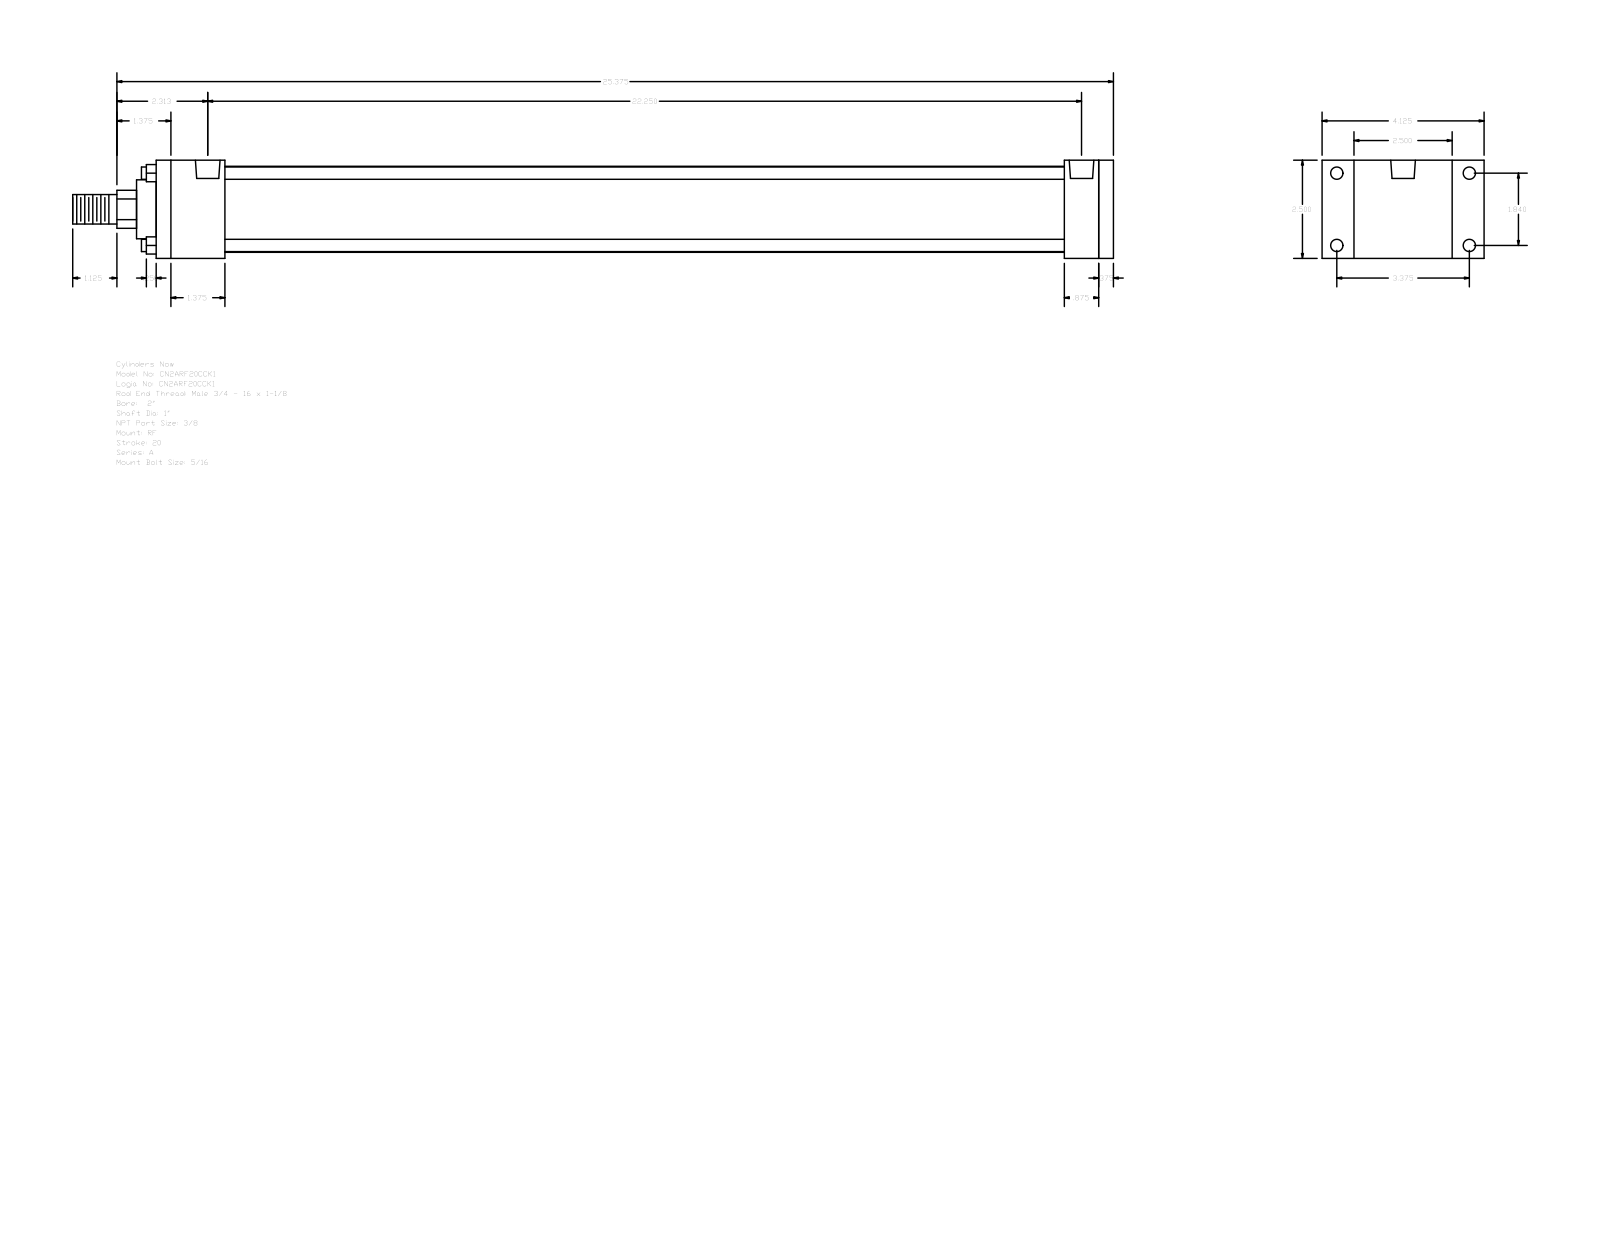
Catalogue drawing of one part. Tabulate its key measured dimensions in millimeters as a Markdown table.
| quantity | value |
| --- | --- |
| part name | A_RF__0200_1 |
| STEP written by | GSSL Pune (CONFIG_CONTROL_DESIGN) |
| units | millimeters |
| bodies | 0 solids, 92 faces (64 planar, 28 cylindrical, 0 other) |
| overall size | 673.1 × 104.78 × 63.5 |
| round holes (diameter × count) | 5.56 × 4, 7.94 × 4, 15.93 × 2 |
| round bosses / shafts (diameter × count) | 7.94 × 4, 55.63 × 1, 38.1 × 1, 25.4 × 1, 19.05 × 1 |
| partial cylindrical surfaces (radius × count) | 12.29 × 1 |
| main face-to-face distances | 63.5, 9.52, 619.12, 609.6, 44.45, 20.64, 565.15, 574.67, 587.37, 542.92 |
| hole center spacings | 46.74, 85.72, 97.63, 559.58, 1.59, 3.98, 561.17, 563.56 |
